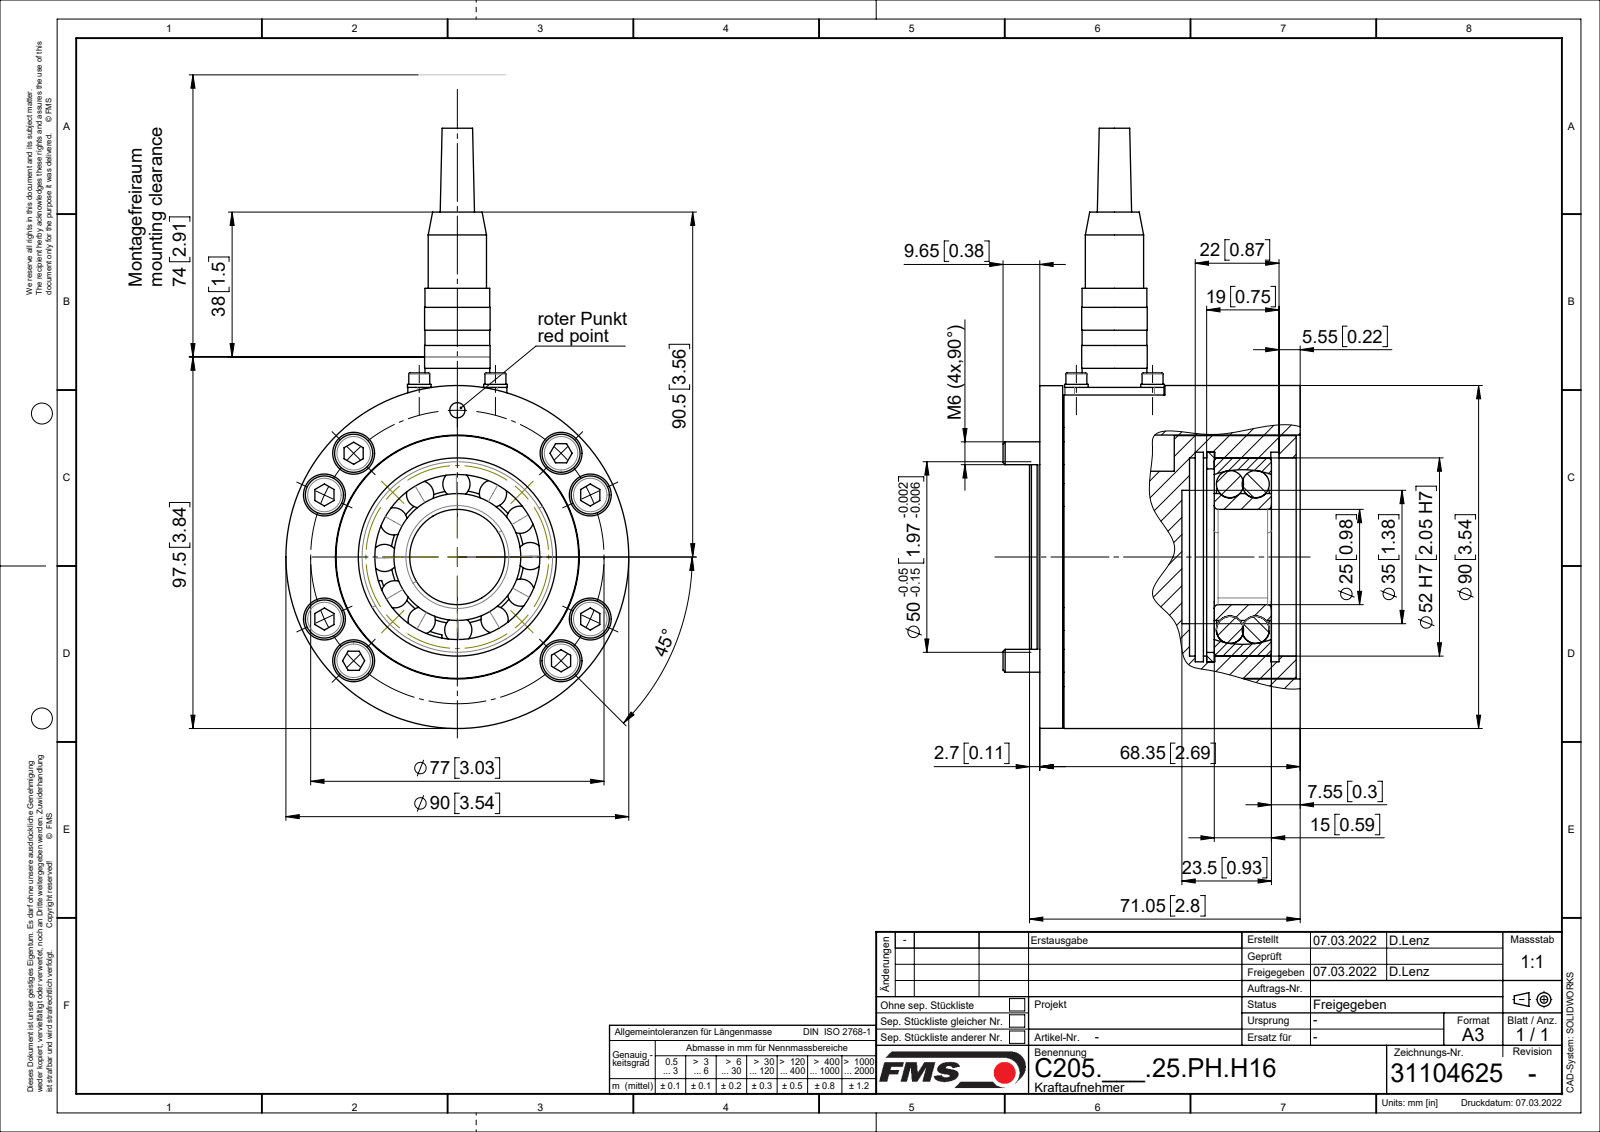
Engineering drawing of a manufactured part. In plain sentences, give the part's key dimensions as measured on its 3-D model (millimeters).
The part is named "Kabeldose_M14x1_Mini_5pol; Si-Ring DIN472_D52x2; Zyl-Schr DIN912_M6x30; Federringe_DIN127A_M03 (+8 more)". Its 3-D file was written by "SolidWorks 2018 (CONFIG_CONTROL_DESIGN)". It is 48 solids with 630 faces: 206 planar, 260 cylindrical and 164 other. Overall it measures 157.5 by 90 by 78 millimeters. Its volume is 307 329 cubic millimeters and its surface area 123 450 square millimeters. Round holes: 8 of diameter 6.5, 8 of diameter 11, 6 of diameter 2.5, 4 of diameter 3.1, 4 of diameter 3.2, 4 of diameter 5, 4 of diameter 7, 2 of diameter 4, 1 of diameter 10.2, 1 of diameter 12, 1 of diameter 15, 1 of diameter 18. Round bosses or shafts: 8 of diameter 10, 8 of diameter 6, 5 of diameter 1.5, 4 of diameter 6.2, 4 of diameter 5.5, 4 of diameter 3, 1 of diameter 90, 1 of diameter 89.9. Partial cylindrical surfaces (rounded edges, fillets, slot ends): 4 of radius 0.1, 4 of radius 2.5, 2 of radius 4.24, 2 of radius 5, 1 of radius 20.8, 1 of radius 24.1. The main face-to-face distances are 6, 3.3, 2.7, 2, 6.5, 32, 33.05, 38, 30, 29.3. The hole center spacings are 20, 38.5, 13.37, 14.14, 38.49, 44.16, 54.44, 63.07.
